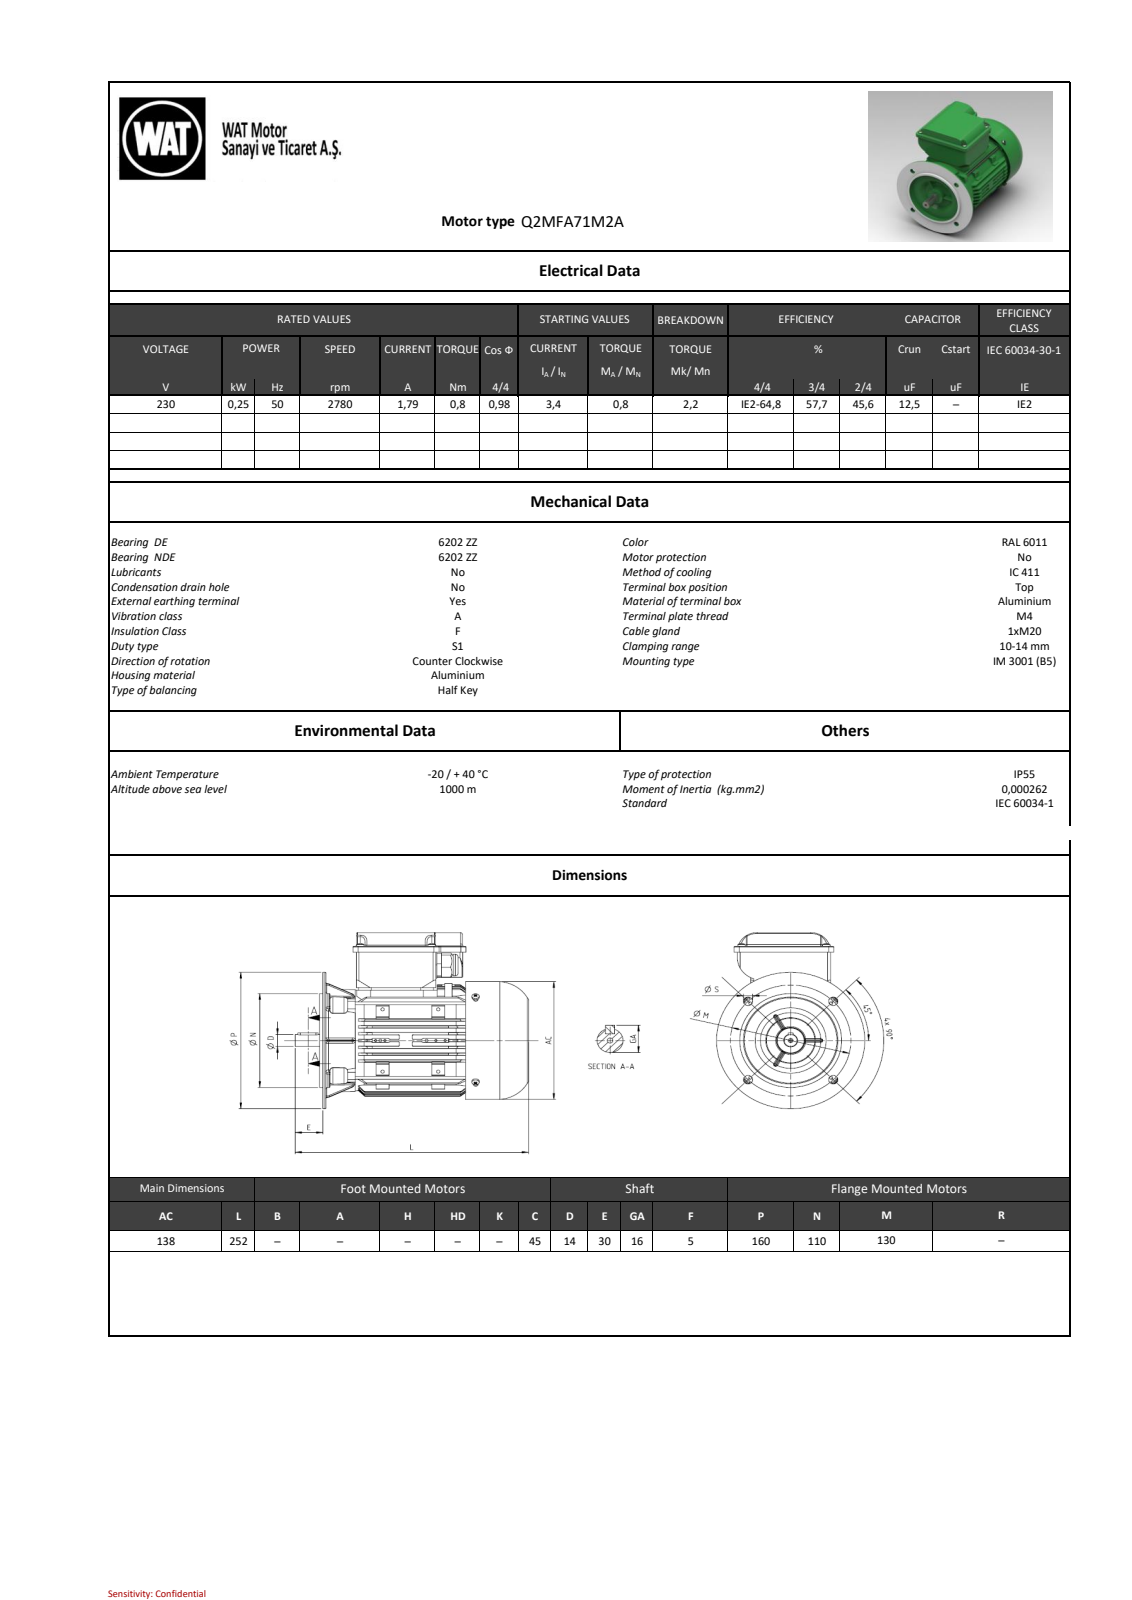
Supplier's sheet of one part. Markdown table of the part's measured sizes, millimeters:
| quantity | value |
| --- | --- |
| part name | BY6434017xx_004-TK_QM63-80; BY6424130xx_004-TKK_QM63-80; BY6432282xx_005-MOTOR_KAPAGI_QS71FA_ISLEME_YENI; 641304741_AZ-KAMA PARALEL A 5x5x22 St50 DIN6885 (+7 more) |
| STEP written by | SIEMENS PLM Software NX2206.8101 (AUTOMOTIVE_DESIGN) |
| units | millimeters |
| bodies | 24 solids, 2905 faces (1253 planar, 765 cylindrical, 887 other) |
| overall size | 252 × 206.5 × 160 |
| volume | 735 633 mm³ |
| surface area | 486 881 mm² |
| round holes (diameter × count) | 3.3 × 13, 3.65 × 8, 4.5 × 8, 2.5 × 6, 4.65 × 4, 4.8 × 4, 10 × 4, 3 × 3, 3.7 × 3, 4.6 × 2, 5 × 1, 6 × 1 |
| round bosses / shafts (diameter × count) | 8 × 8, 4 × 8, 3 × 8, 160 × 1, 138 × 1, 136 × 1, 110 × 1, 26 × 1 |
| partial cylindrical surfaces (radius × count) | 1 × 127, 2 × 70, 1.2 × 36, 0.5 × 32, 10 × 24, 0.75 × 18, 2.5 × 14, 4 × 14 |
| main face-to-face distances | 3, 185.5, 2, 177.2, 3.5, 146.5, 5, 30.7, 4, 64.5 |
| hole center spacings | 89.74, 55, 36.59, 65, 60, 3.13, 37.26, 61.87 |
